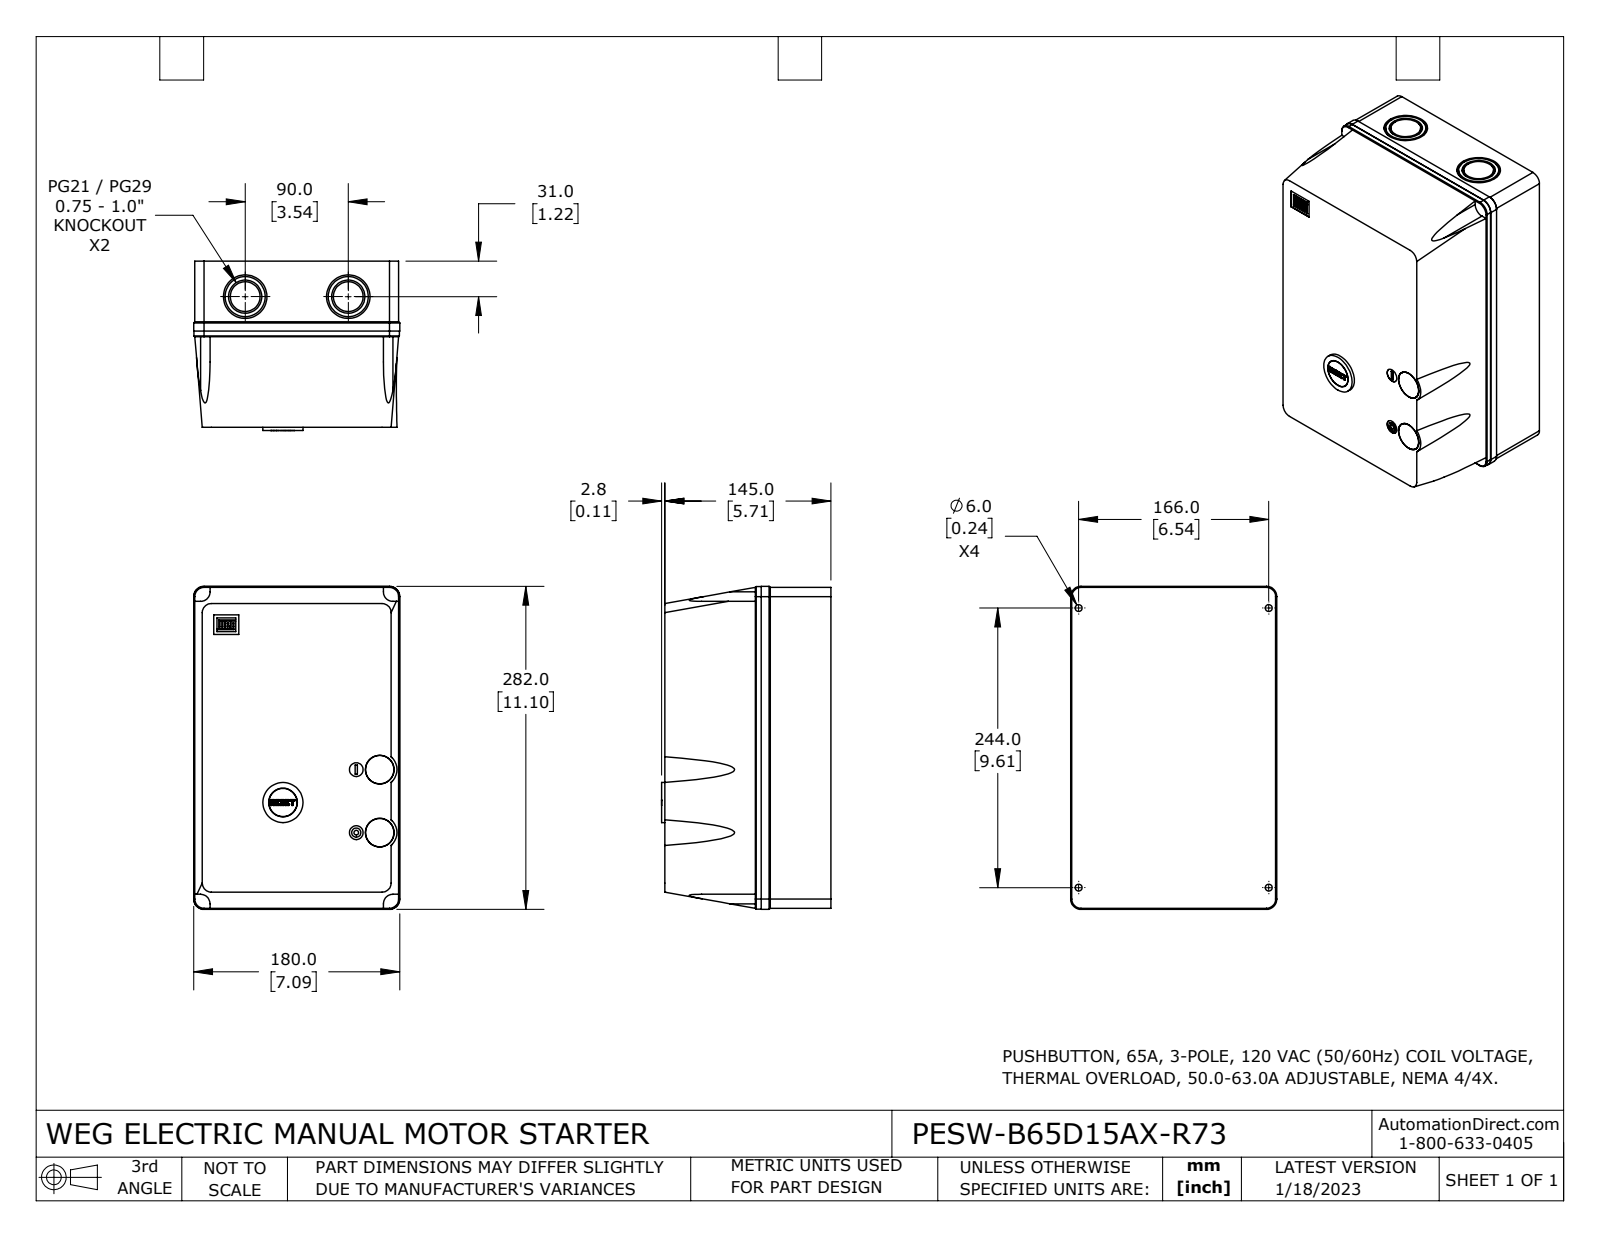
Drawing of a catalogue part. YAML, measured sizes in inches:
part_name: "PESW-B65D15AX-R73"
step_written_by: "SolidWorks 2021 (CONFIG_CONTROL_DESIGN)"
units: inches
bodies: {solids: 3, faces: 286, planar: 130, cylindrical: 144, other: 12}
overall_size: [11.102, 7.087, 5.823]
volume: 428
surface_area: 360
round_holes:
  - {diameter: 0.236, count: 4}
  - {diameter: 0.984, count: 3}
  - {diameter: 0.472, count: 2}
  - {diameter: 1.142, count: 2}
  - {diameter: 1.496, count: 2}
  - {diameter: 0.157, count: 1}
  - {diameter: 1.201, count: 1}
round_bosses_or_shafts:
  - {diameter: 1.378, count: 3}
  - {diameter: 1.024, count: 2}
  - {diameter: 0.976, count: 2}
  - {diameter: 1.193, count: 1}
  - {diameter: 0.969, count: 1}
  - {diameter: 0.551, count: 1}
  - {diameter: 0.315, count: 1}
partial_cylinders:
  - {radius: 0.004, count: 34}
  - {radius: 0.315, count: 4}
  - {radius: 0.327, count: 4}
  - {radius: 0.343, count: 4}
  - {radius: 0.354, count: 4}
  - {radius: 0.063, count: 1}
face_to_face_distances: [5.709, 7.008, 11.024, 0.039, 0.028, 7.047, 7.075, 7.035, 11.063, 7.087]
hole_center_spacings: [0.807, 2.165, 2.311, 6.535, 9.606, 11.619, 1.935, 2.25]
